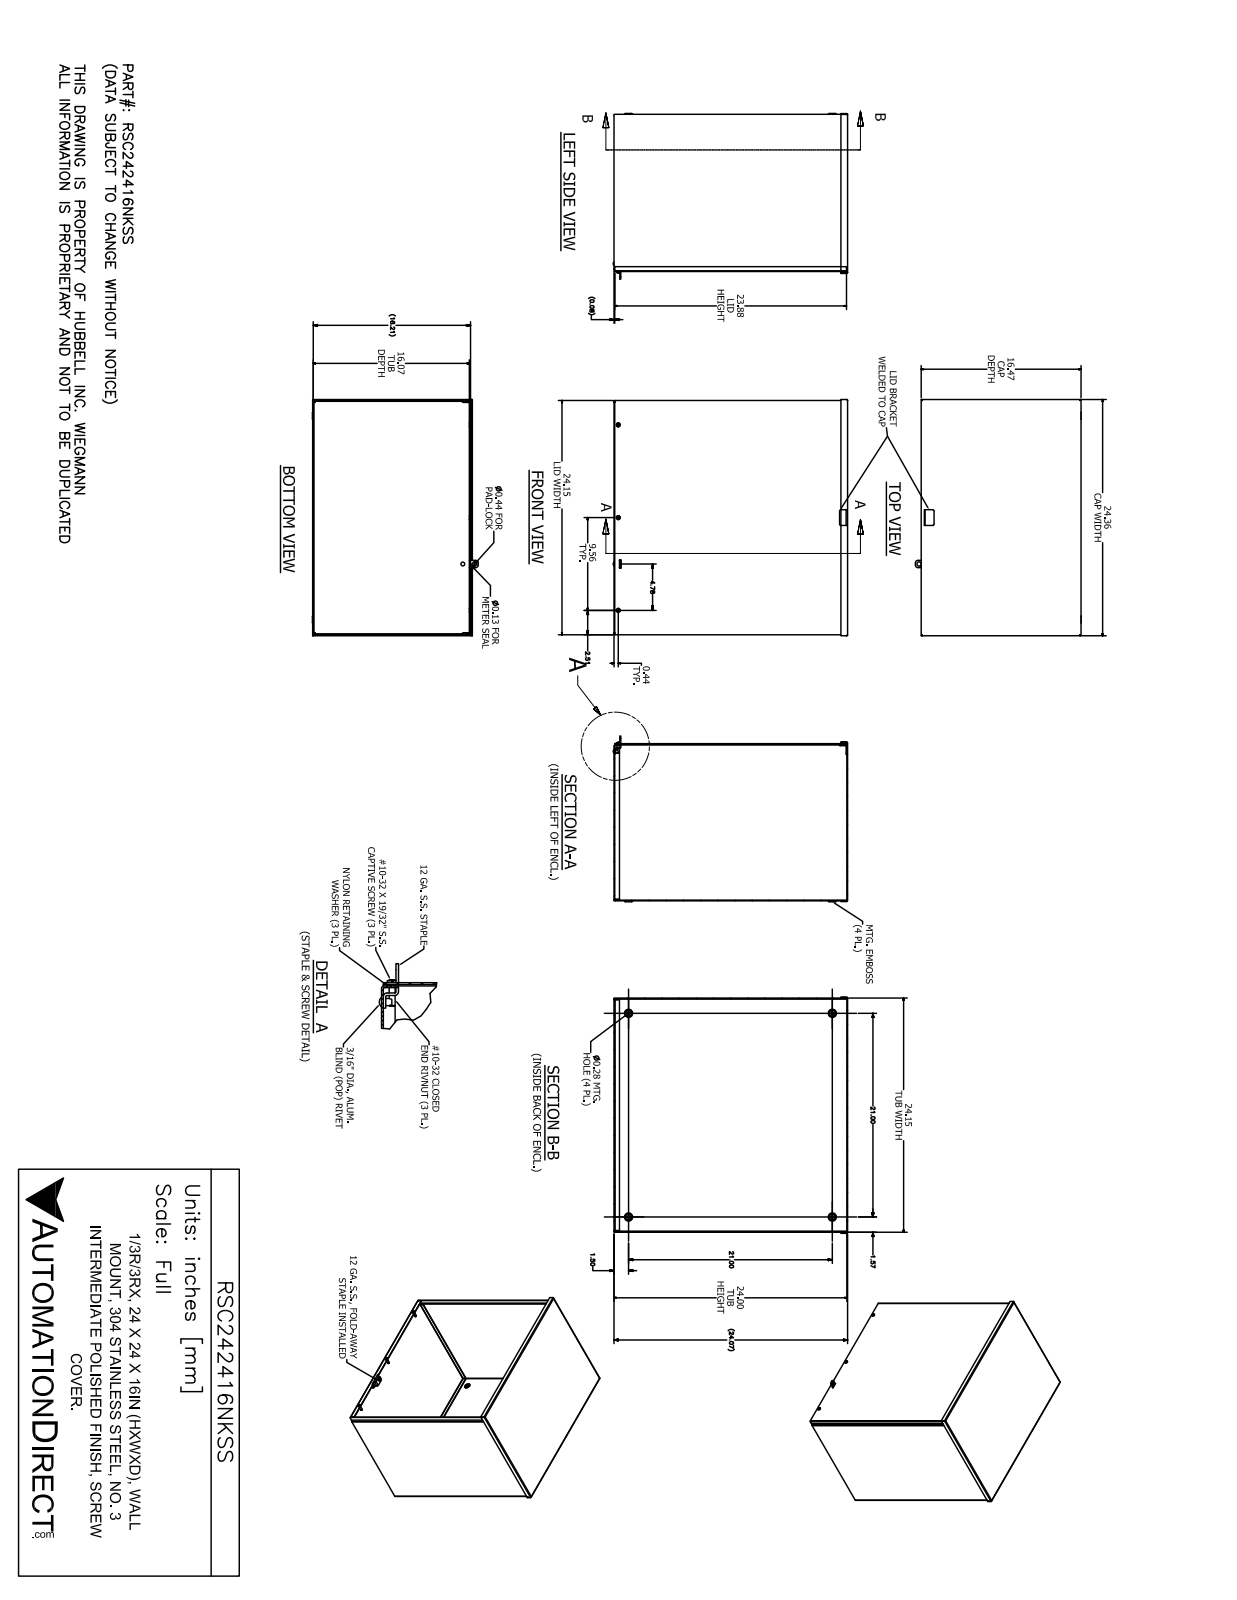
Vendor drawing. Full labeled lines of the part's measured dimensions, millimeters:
Part name (STEP PRODUCT): RSC242416NKSS
STEP written by: SolidWorks 2017 (AUTOMOTIVE_DESIGN)
Units: millimetres
Bodies: 16 solids, 458 faces (237 planar, 113 cylindrical, 108 other)
Overall size (bounding box): 618.7 × 613.8 × 433.9
Volume: 3 420 000 mm³ · Surface area: 3 662 000 mm²
Round holes (diameter × count): ⌀6.4 ×6, ⌀7.1 ×4, ⌀4 ×3, ⌀5 ×3, ⌀6.5 ×3, ⌀7.1 ×3, ⌀3.2 ×1, ⌀5 ×1, ⌀5.1 ×1, ⌀11.1 ×1
Round bosses / shafts (diameter × count): ⌀11.5 ×3, ⌀10.3 ×3, ⌀6.3 ×3, ⌀4.2 ×3, ⌀4.7 ×1
Partial cylindrical surfaces — rounded edges, fillets, slot ends (radius × count): R0.8 ×23, R2.7 ×17, R3.2 ×4, R6.4 ×4, R1.6 ×3, R1.6 ×3, R2.3 ×3, R1.2 ×2
Main face-to-face distances: 1.9, 409.8, 609.6, 611.5, 411.6, 407.9, 607.7, 613.4, 2.9, 608.6
Hole centre spacings: 242.9, 533.4, 636.3, 588.2, 36, 36.6, 268.1, 268.1
